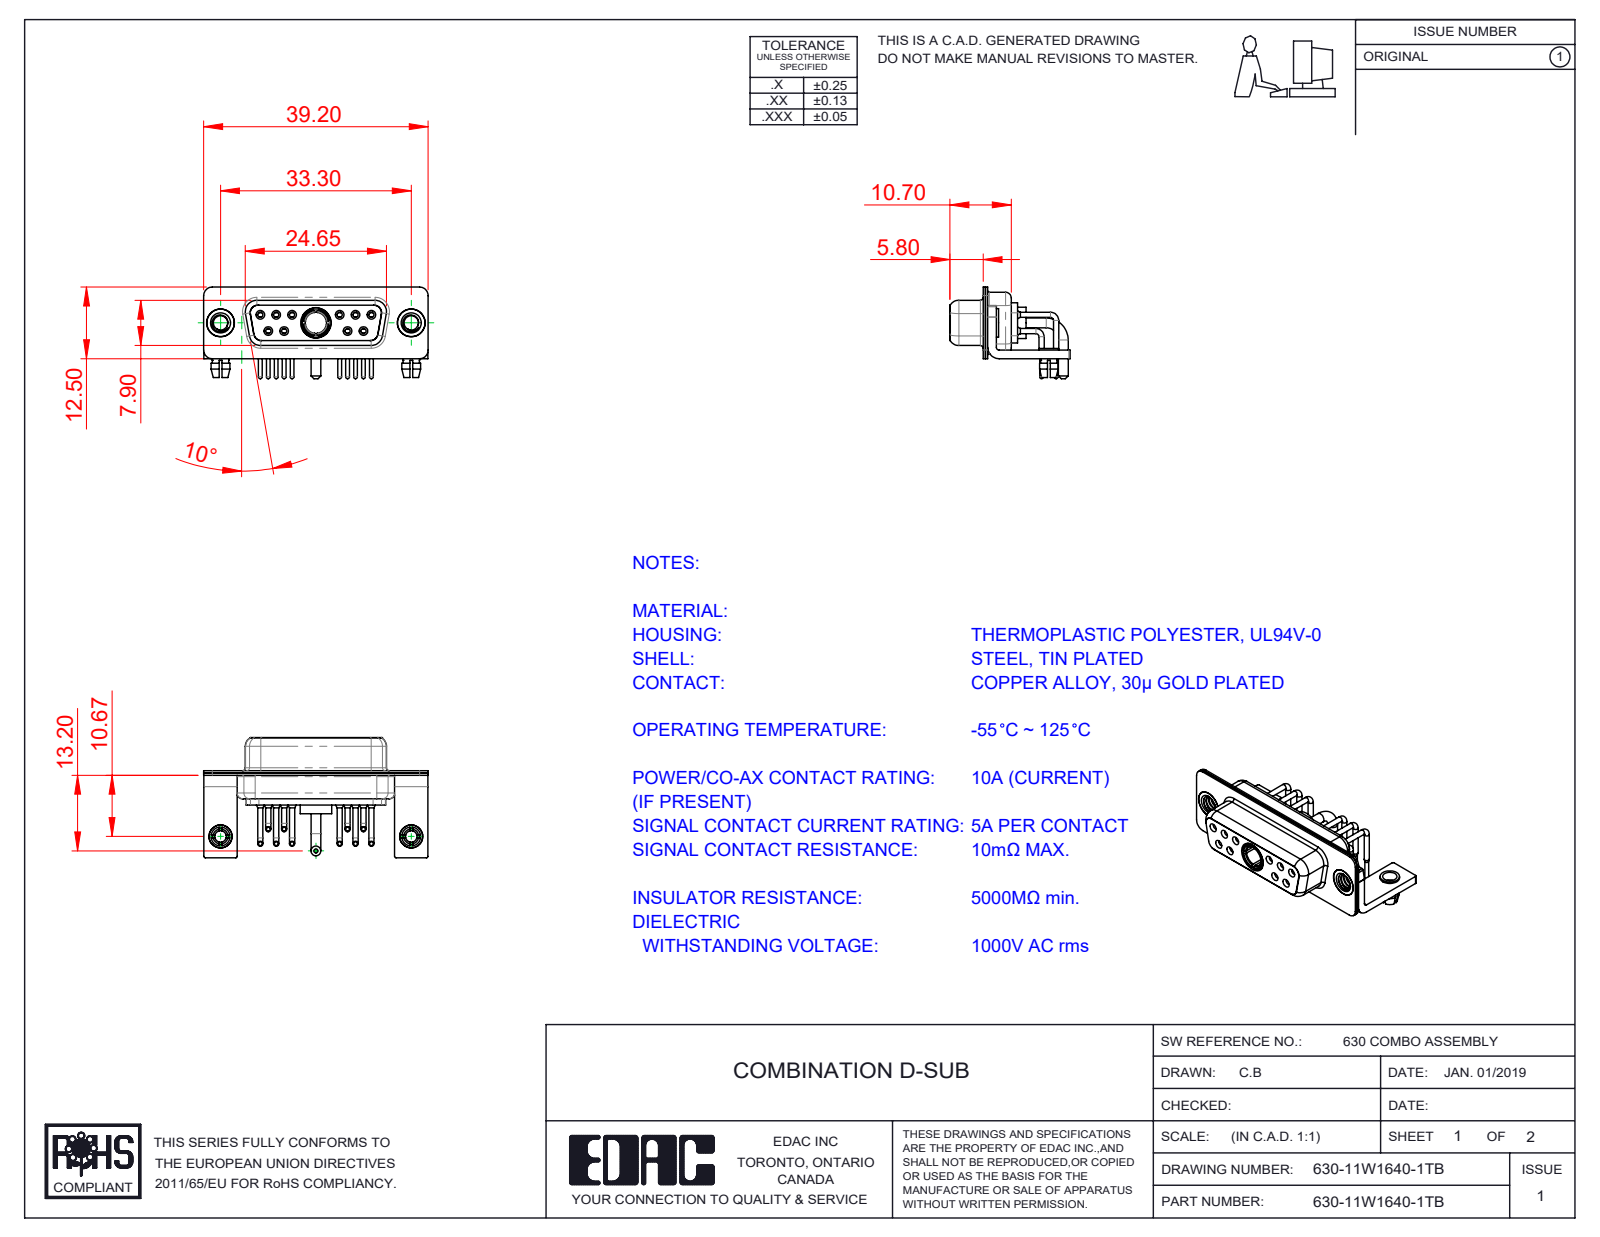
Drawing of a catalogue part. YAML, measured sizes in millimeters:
part_name: "Power Socket_10A RA; 630Combo Stabilizer Bracket; 630Combo Contact Row 2; 630Combo Contact Row 1 (+6 more)"
step_written_by: "SolidWorks 2020 (CONFIG_CONTROL_DESIGN)"
units: millimeters
bodies: {solids: 21, faces: 1017, planar: 314, cylindrical: 442, other: 261}
overall_size: [39.2, 21, 16]
volume: 2886
surface_area: 7020
round_holes:
  - {diameter: 2, count: 12}
  - {diameter: 0.9, count: 10}
  - {diameter: 1.1, count: 10}
  - {diameter: 1.5, count: 10}
  - {diameter: 1.7, count: 6}
  - {diameter: 1.6, count: 4}
  - {diameter: 2.5, count: 4}
  - {diameter: 4.85, count: 3}
  - {diameter: 3.2, count: 2}
  - {diameter: 4, count: 2}
  - {diameter: 4.05, count: 2}
  - {diameter: 3.7, count: 1}
round_bosses_or_shafts:
  - {diameter: 0.9, count: 10}
  - {diameter: 0.65, count: 10}
  - {diameter: 1.6, count: 6}
  - {diameter: 5, count: 2}
  - {diameter: 4.95, count: 2}
  - {diameter: 4.8, count: 2}
  - {diameter: 4, count: 2}
  - {diameter: 3.4, count: 2}
partial_cylinders:
  - {radius: 0.25, count: 16}
  - {radius: 1.5, count: 16}
  - {radius: 2, count: 13}
  - {radius: 1.35, count: 12}
  - {radius: 1.6, count: 8}
  - {radius: 0.5, count: 5}
  - {radius: 0.6, count: 4}
  - {radius: 0.65, count: 4}
face_to_face_distances: [0.4, 0.8, 0.45, 1.4, 8.45, 1.5, 1.8, 8.9, 6.2, 2.3]
hole_center_spacings: [3.16, 2.77, 13.85, 11.08, 16.62, 5.03, 5.04, 5.54]
